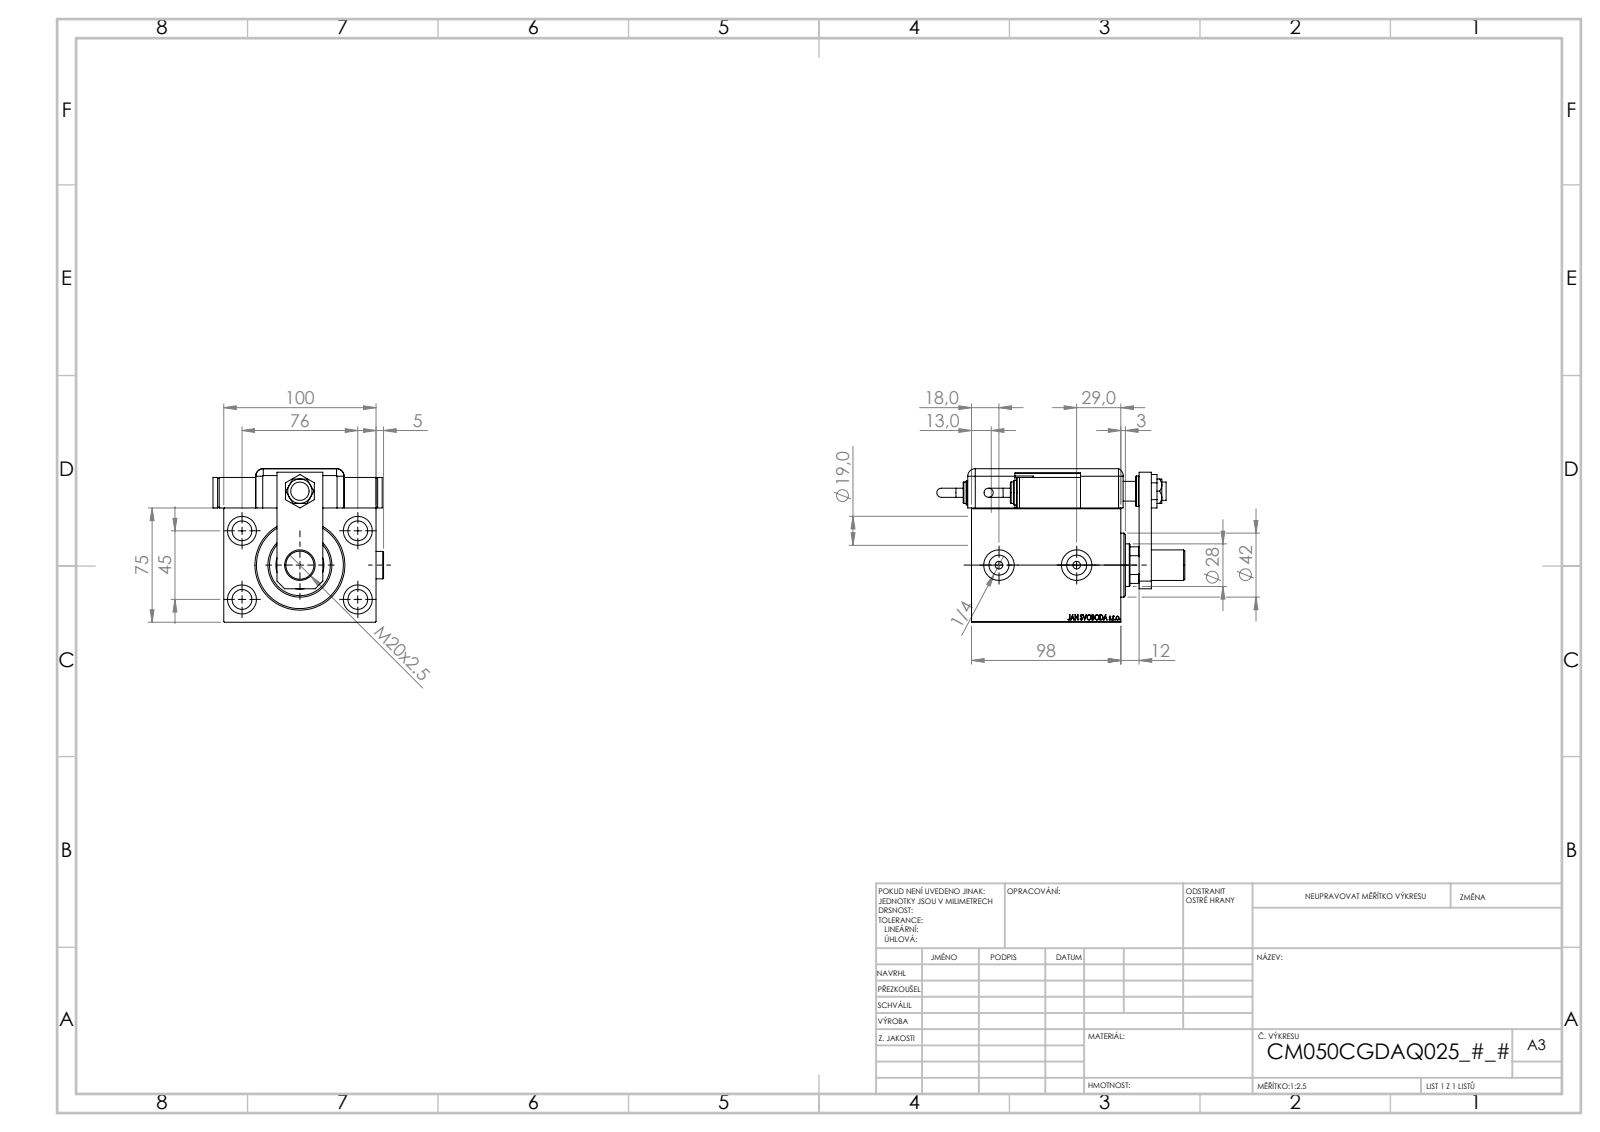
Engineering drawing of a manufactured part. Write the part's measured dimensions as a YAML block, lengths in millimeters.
part_name: "KRYT; V450CM_MALE_METRIC; V450CM_C_VCP; V450CM_VC_B (+7 more)"
step_written_by: "SolidWorks 2019 (CONFIG_CONTROL_DESIGN)"
units: millimeters
bodies: {solids: 16, faces: 1317, planar: 653, cylindrical: 137, other: 527}
overall_size: [162.76, 111.9, 100.8]
volume: 780161
surface_area: 165542
round_holes:
  - {diameter: 13, count: 5}
  - {diameter: 19, count: 4}
  - {diameter: 20, count: 3}
  - {diameter: 4, count: 2}
  - {diameter: 5, count: 2}
  - {diameter: 8, count: 2}
  - {diameter: 13.16, count: 2}
  - {diameter: 12, count: 1}
  - {diameter: 14, count: 1}
  - {diameter: 18.5, count: 1}
  - {diameter: 28, count: 1}
  - {diameter: 31.5, count: 1}
round_bosses_or_shafts:
  - {diameter: 20, count: 3}
  - {diameter: 18, count: 3}
  - {diameter: 16, count: 2}
  - {diameter: 14, count: 2}
  - {diameter: 6, count: 2}
  - {diameter: 42, count: 1}
partial_cylinders:
  - {radius: 5, count: 9}
  - {radius: 10, count: 1}
  - {radius: 13.5, count: 1}
face_to_face_distances: [75, 3, 100, 98, 14, 20, 13.5, 84, 25.8, 100.8]
hole_center_spacings: [44.16, 45, 46.04, 76, 80.53, 88.32, 20, 48.5]
